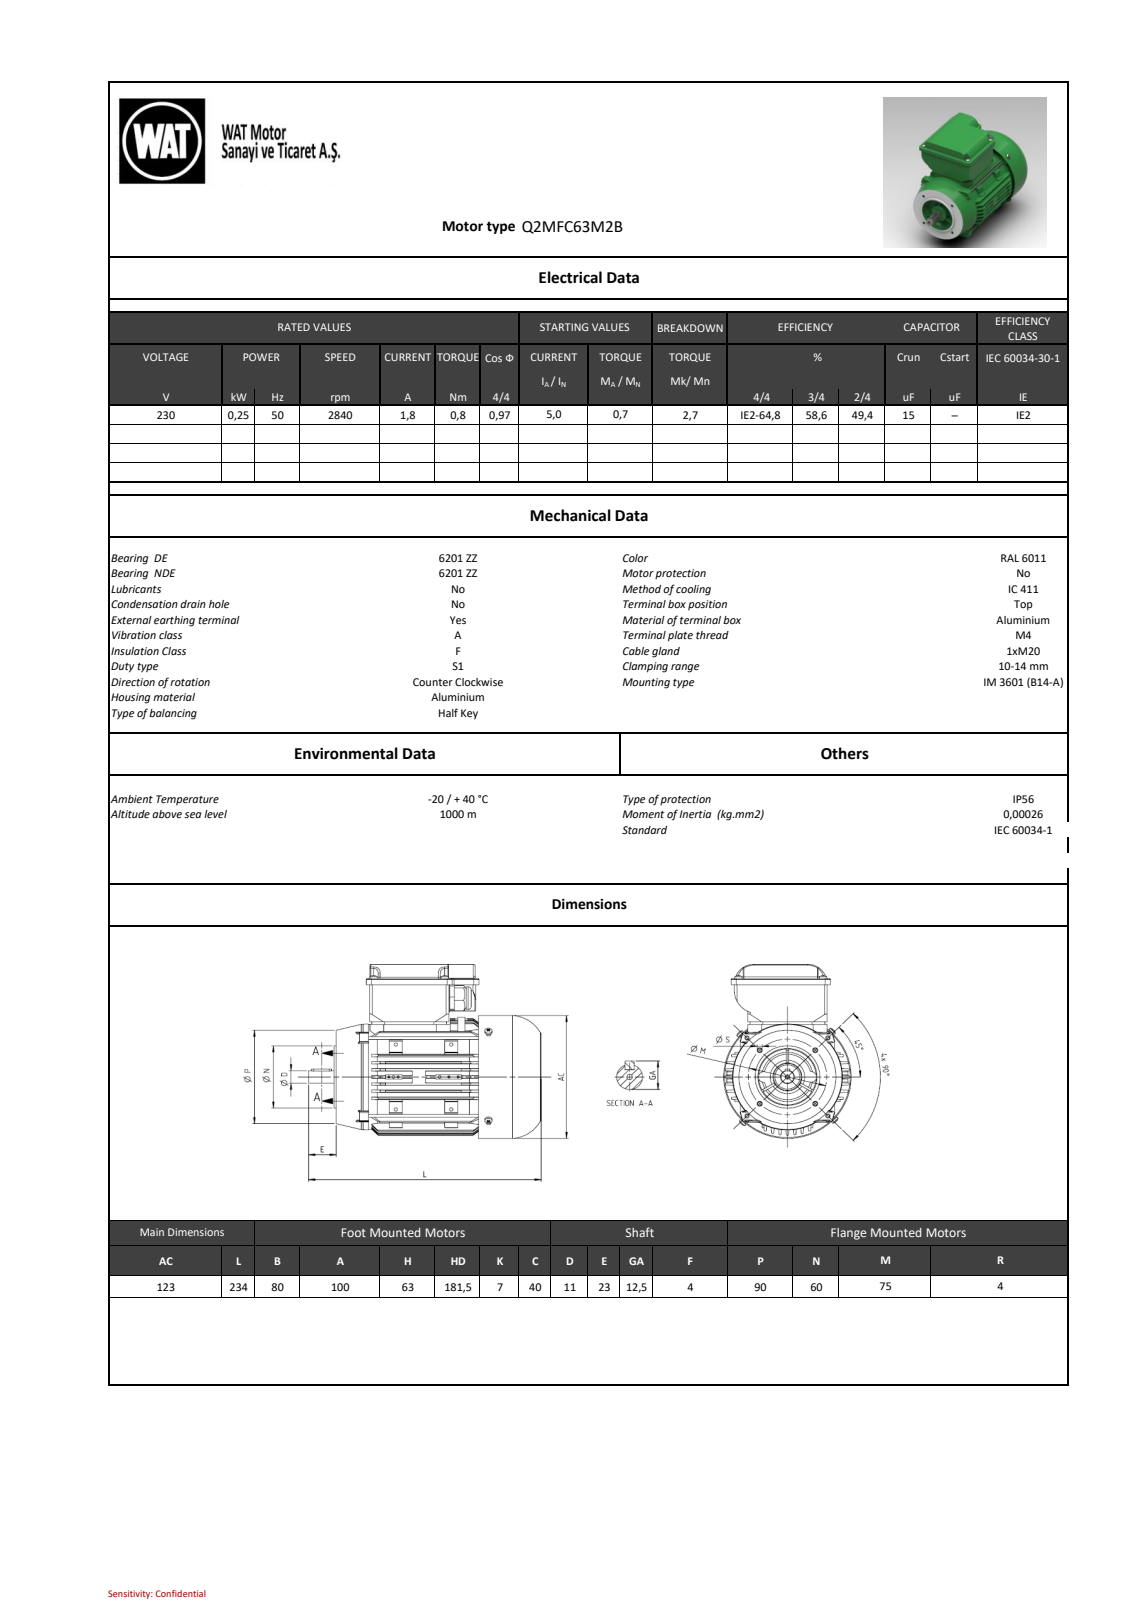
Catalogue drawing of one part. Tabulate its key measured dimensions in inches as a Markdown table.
| quantity | value |
| --- | --- |
| part name | BY6434017xx_004-TK_QM63-80; BY6424130xx_004-TKK_QM63-80; BY6424111xx_004-MOTOR_KAPAGI_QS63FC_ISLEME; BY6423003xx_006-FAN_KAPAGI_QS63 (+6 more) |
| STEP written by | SIEMENS PLM Software NX2206.8101 (AUTOMOTIVE_DESIGN) |
| units | inches |
| bodies | 34 solids, 2042 faces (1073 planar, 705 cylindrical, 264 other) |
| overall size | 9.192 × 7.087 × 4.843 |
| volume | 34.7 in³ |
| surface area | 632.7 in² |
| round holes (diameter × count) | 0.144 × 10, 0.13 × 9, 0.177 × 8, 0.098 × 6, 0.15 × 4, 0.157 × 4, 0.183 × 4, 0.189 × 4, 0.118 × 3, 0.197 × 1, 0.315 × 1, 0.402 × 1 |
| round bosses / shafts (diameter × count) | 0.315 × 8, 0.157 × 8, 0.118 × 8, 0.189 × 4, 4.843 × 1, 4.764 × 1, 3.898 × 1, 2.362 × 1 |
| partial cylindrical surfaces (radius × count) | 0.02 × 210, 0.039 × 67, 0.079 × 50, 0.197 × 26, 0.098 × 20, 0.157 × 11, 0.118 × 9, 0.217 × 9 |
| main face-to-face distances | 0.118, 0.059, 0.177, 0.276, 1.101, 5.807, 0.039, 1.104, 0.276, 0.271 |
| hole center spacings | 2.165, 2.608, 1.476, 2.126, 2.48, 2.603, 2.634, 3.267 |
